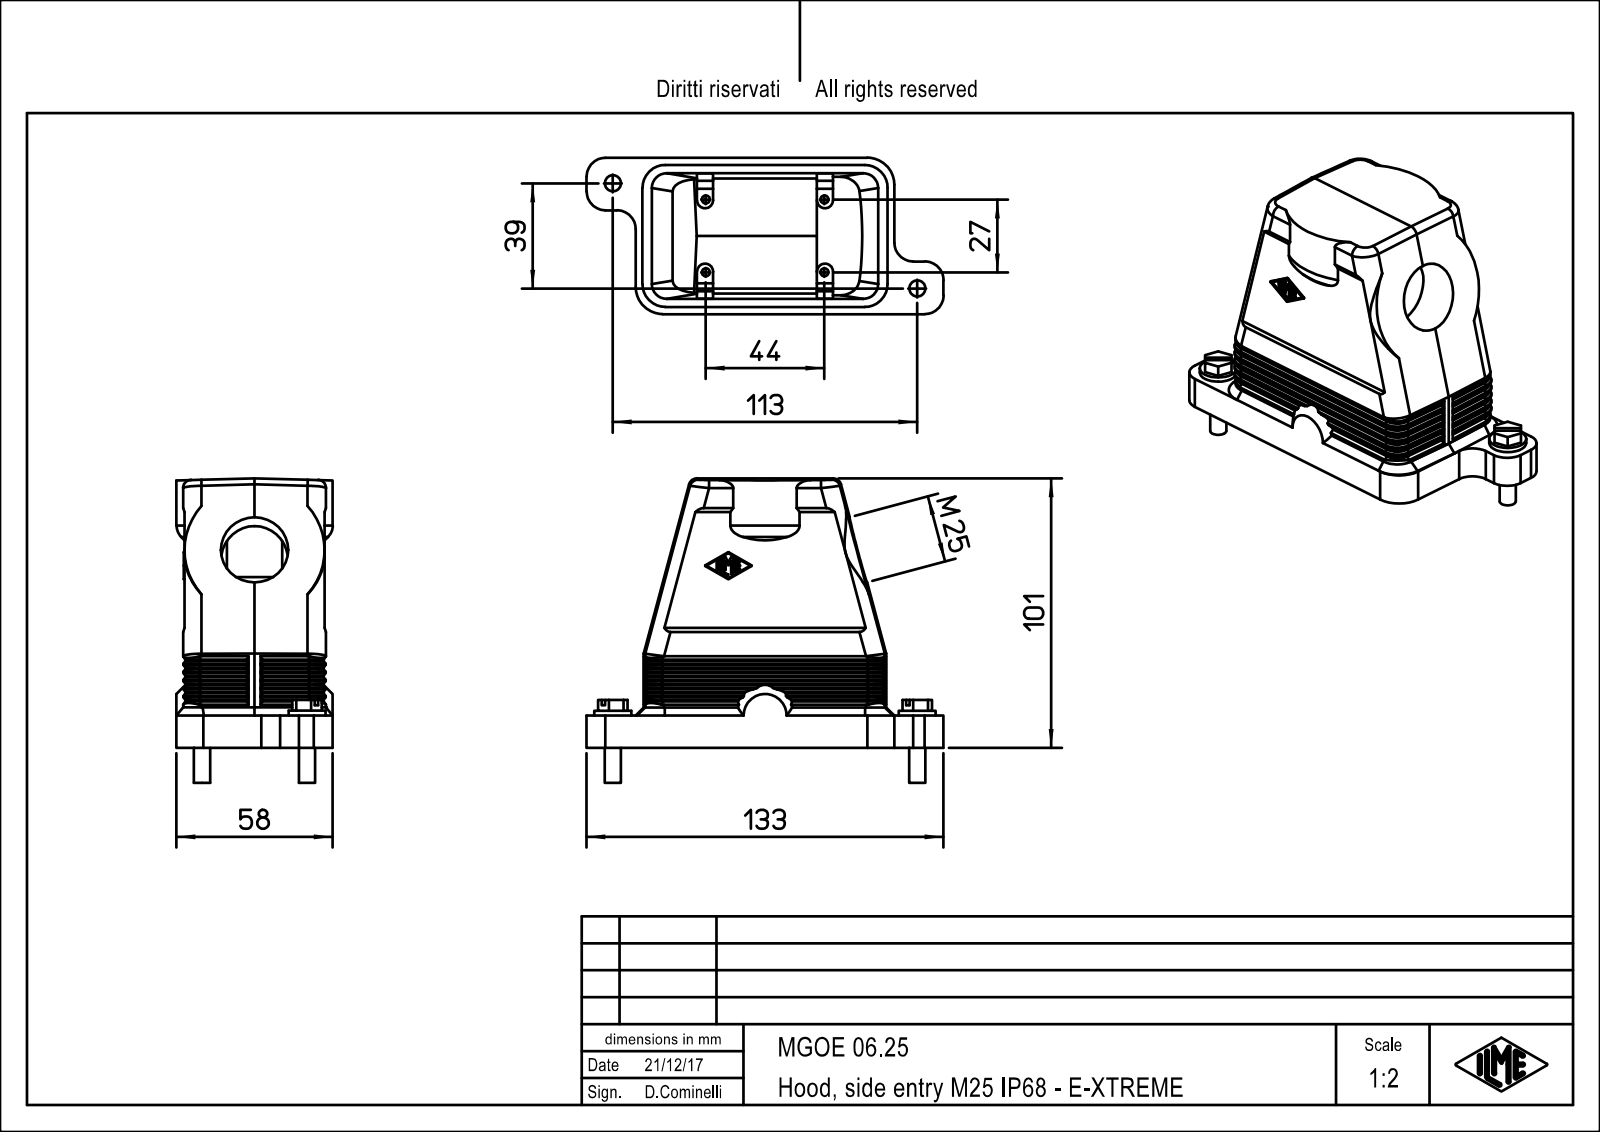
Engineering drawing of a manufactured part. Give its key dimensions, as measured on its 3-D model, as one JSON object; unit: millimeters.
{"part_name": "MGOE_06.25", "step_written_by": "PTC Creo Elements/Direct Modeling 19.0E 27-Jun-2016 (C) Parametric Technology GmbH (AUTOMOTIVE_DESIGN)", "units": "millimeters", "bodies": {"solids": 1, "faces": 509, "planar": 245, "cylindrical": 202, "other": 62}, "overall_size": [132.5, 113, 58], "volume_mm3": 146733, "surface_area_mm2": 63677, "round_holes": [[3, 4], [25, 1]], "round_bosses_or_shafts": [[13.7, 2], [6, 2]], "partial_cylinders_radius": [[0.5, 66], [7, 62], [0.33, 15], [3, 6], [5.5, 4], [8.5, 4], [0.17, 3], [10, 2]], "face_to_face_distances": [3, 55, 52, 2.5, 6, 44.5, 3.33, 0.5, 55.5, 52.5], "hole_center_spacings": [27, 44, 51.62]}
